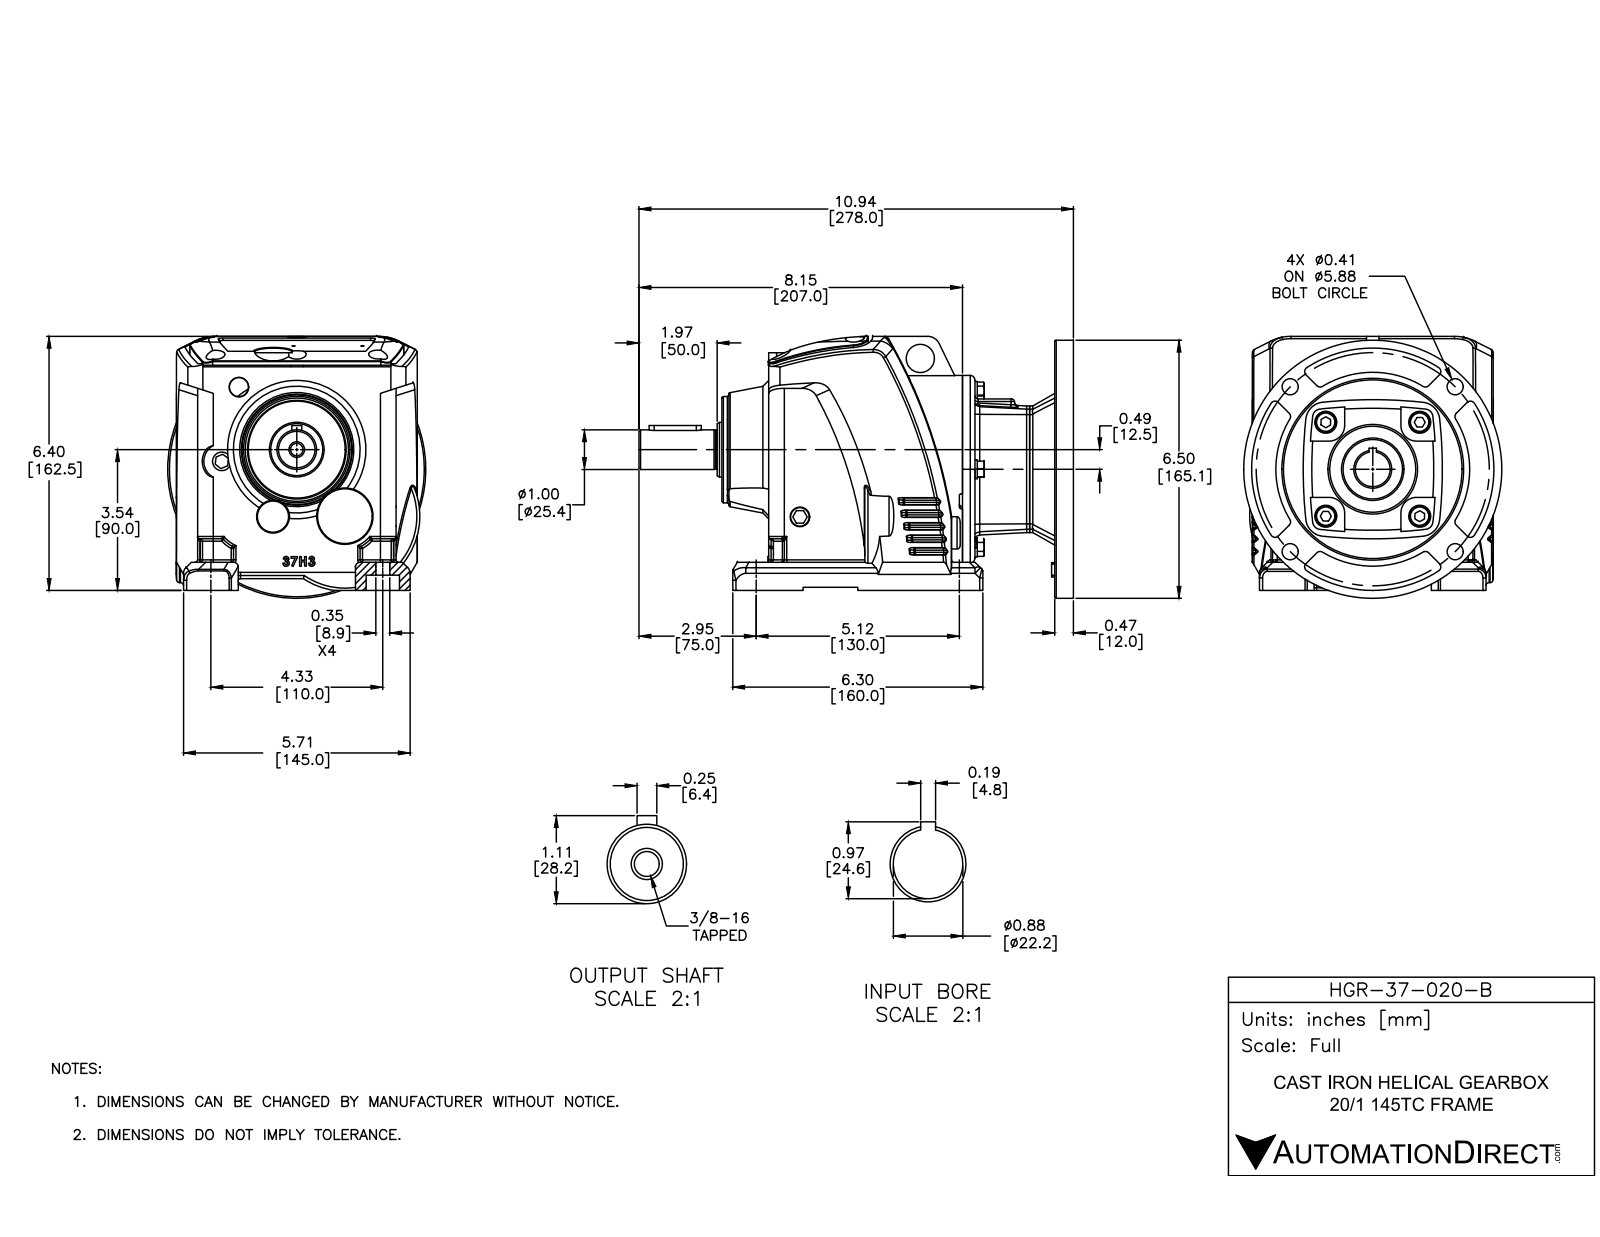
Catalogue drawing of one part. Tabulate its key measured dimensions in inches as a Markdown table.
| quantity | value |
| --- | --- |
| part name | HGR-37-020-B |
| STEP written by | SolidWorks 2015 (CONFIG_CONTROL_DESIGN) |
| units | inches |
| bodies | 28 solids, 1025 faces (348 planar, 289 cylindrical, 388 other) |
| overall size | 10.945 × 6.596 × 6.5 |
| volume | 187.1 in³ |
| surface area | 478.1 in² |
| round holes (diameter × count) | 0.472 × 6, 0.406 × 4, 0.551 × 4, 0.276 × 3, 0.079 × 2, 0.354 × 2, 0.394 × 2, 0.313 × 1, 0.53 × 1, 0.709 × 1, 0.875 × 1, 1.378 × 1 |
| round bosses / shafts (diameter × count) | 0.512 × 7, 0.48 × 4, 6.5 × 1, 4.724 × 1, 2.677 × 1, 2.441 × 1, 2.165 × 1, 1.378 × 1 |
| partial cylindrical surfaces (radius × count) | 0.059 × 43, 0.118 × 19, 0.079 × 18, 0.394 × 10, 0.197 × 8, 0.315 × 5, 0.157 × 4, 0.276 × 4 |
| main face-to-face distances | 0.276, 0.63, 2.323, 1.102, 7.48, 1.693, 7.205, 0.315, 0.906, 2.598 |
| hole center spacings | 1.264, 1.673, 2.937, 3.38, 3.381, 4.611, 1.37, 1.868 |
